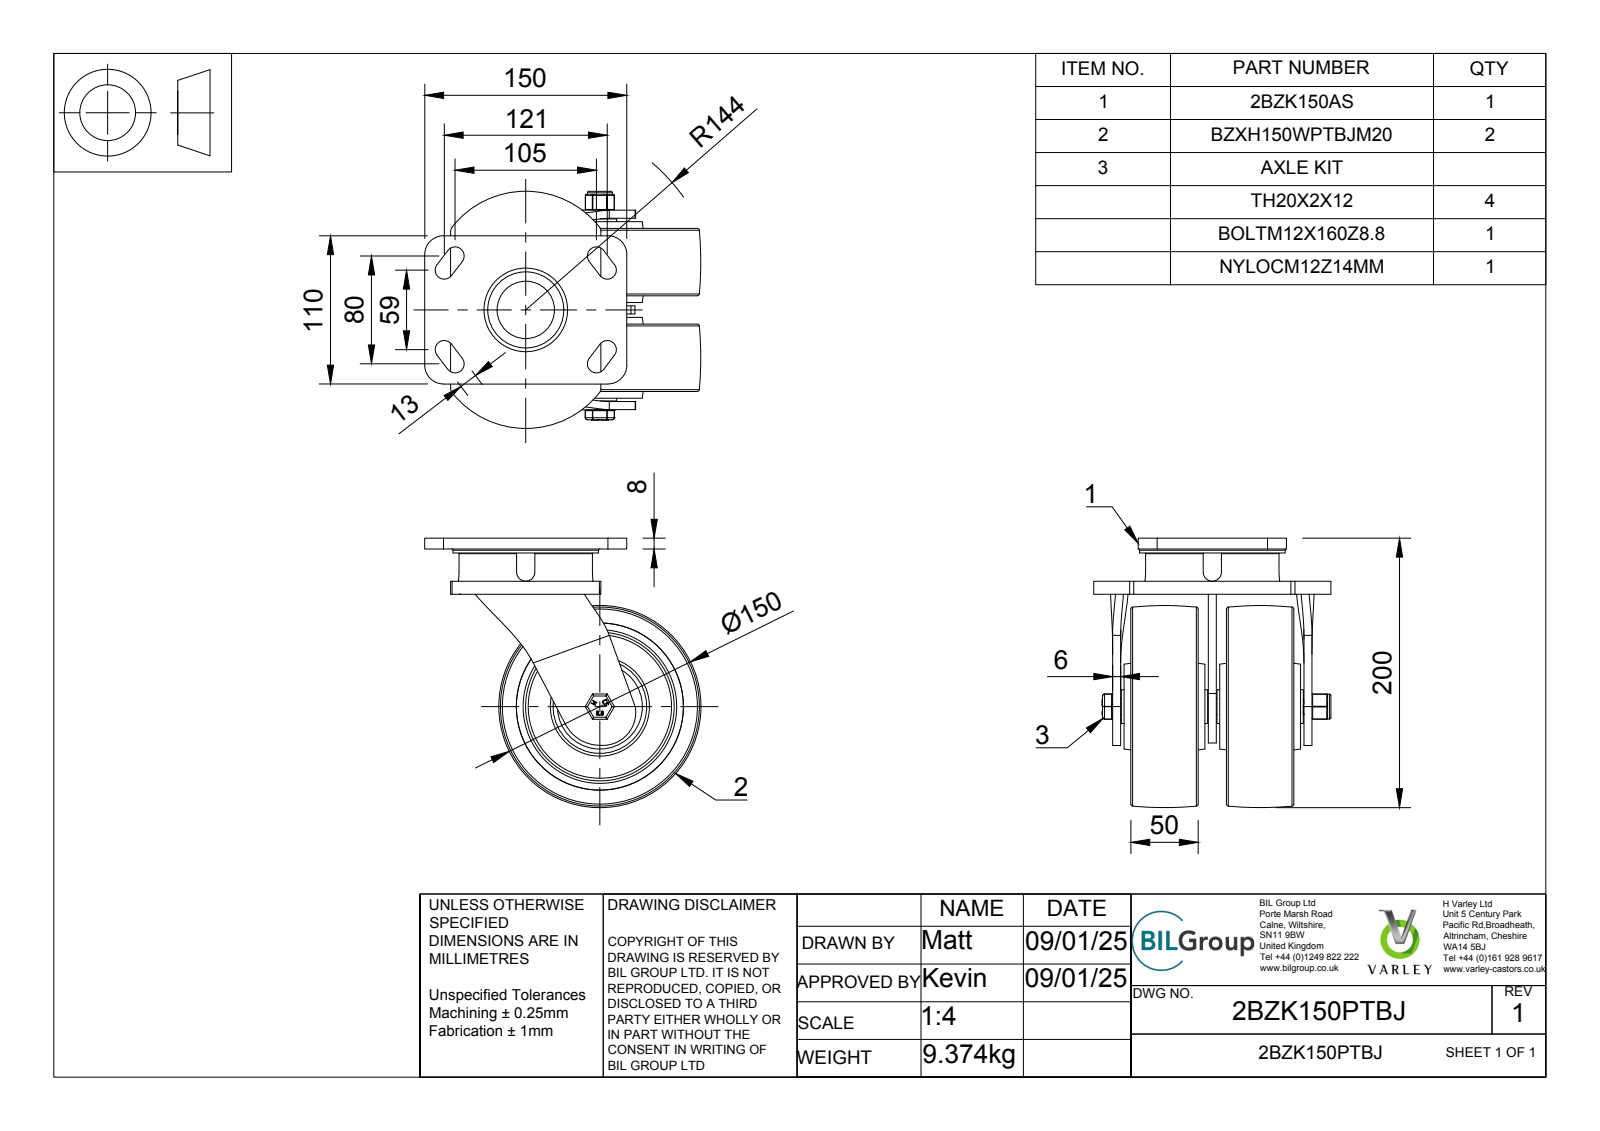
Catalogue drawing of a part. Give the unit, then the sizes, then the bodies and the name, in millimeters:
Units: millimetres
Overall size (bounding box): 205 × 200 × 176
Round holes (diameter × count): ⌀12 ×1, ⌀12.2 ×1, ⌀12.5 ×1, ⌀14 ×1, ⌀20 ×1, ⌀28.5 ×1, ⌀41.5 ×1, ⌀42 ×1, ⌀44 ×1, ⌀47 ×1, ⌀56.5 ×1, ⌀62 ×1
Round bosses / shafts (diameter × count): ⌀108 ×1, ⌀100 ×1, ⌀40.5 ×1, ⌀40 ×1, ⌀29 ×1, ⌀27 ×1, ⌀25 ×1, ⌀24 ×1
Partial cylindrical surfaces — rounded edges, fillets, slot ends (radius × count): R4 ×20, R6 ×20, R0.5 ×18, R0.25 ×12, R6.75 ×10, R1.5 ×6, R0.47 ×4, R0.9 ×4
Main face-to-face distances: 71, 35.5, 6, 7.5, 13.5, 63.5, 22, 57.5, 28, 29.5
Volume: 1 725 000 mm³ · Surface area: 484 060 mm²
Bodies: 67 solids, 2329 faces (1071 planar, 458 cylindrical, 800 other)
Part name (STEP PRODUCT): 2BZK150PTBJ v4; 2BZK150AS v1; FABRICATED STEEL TOP PLATE; FABRICATED STEEL FORKS (+8 more)
STEP written by: Autodesk Translation Framework v13.20.0.188 (AP242_MANAGED_MODEL_BASED_3D_ENGINEERING_MIM_LF)
